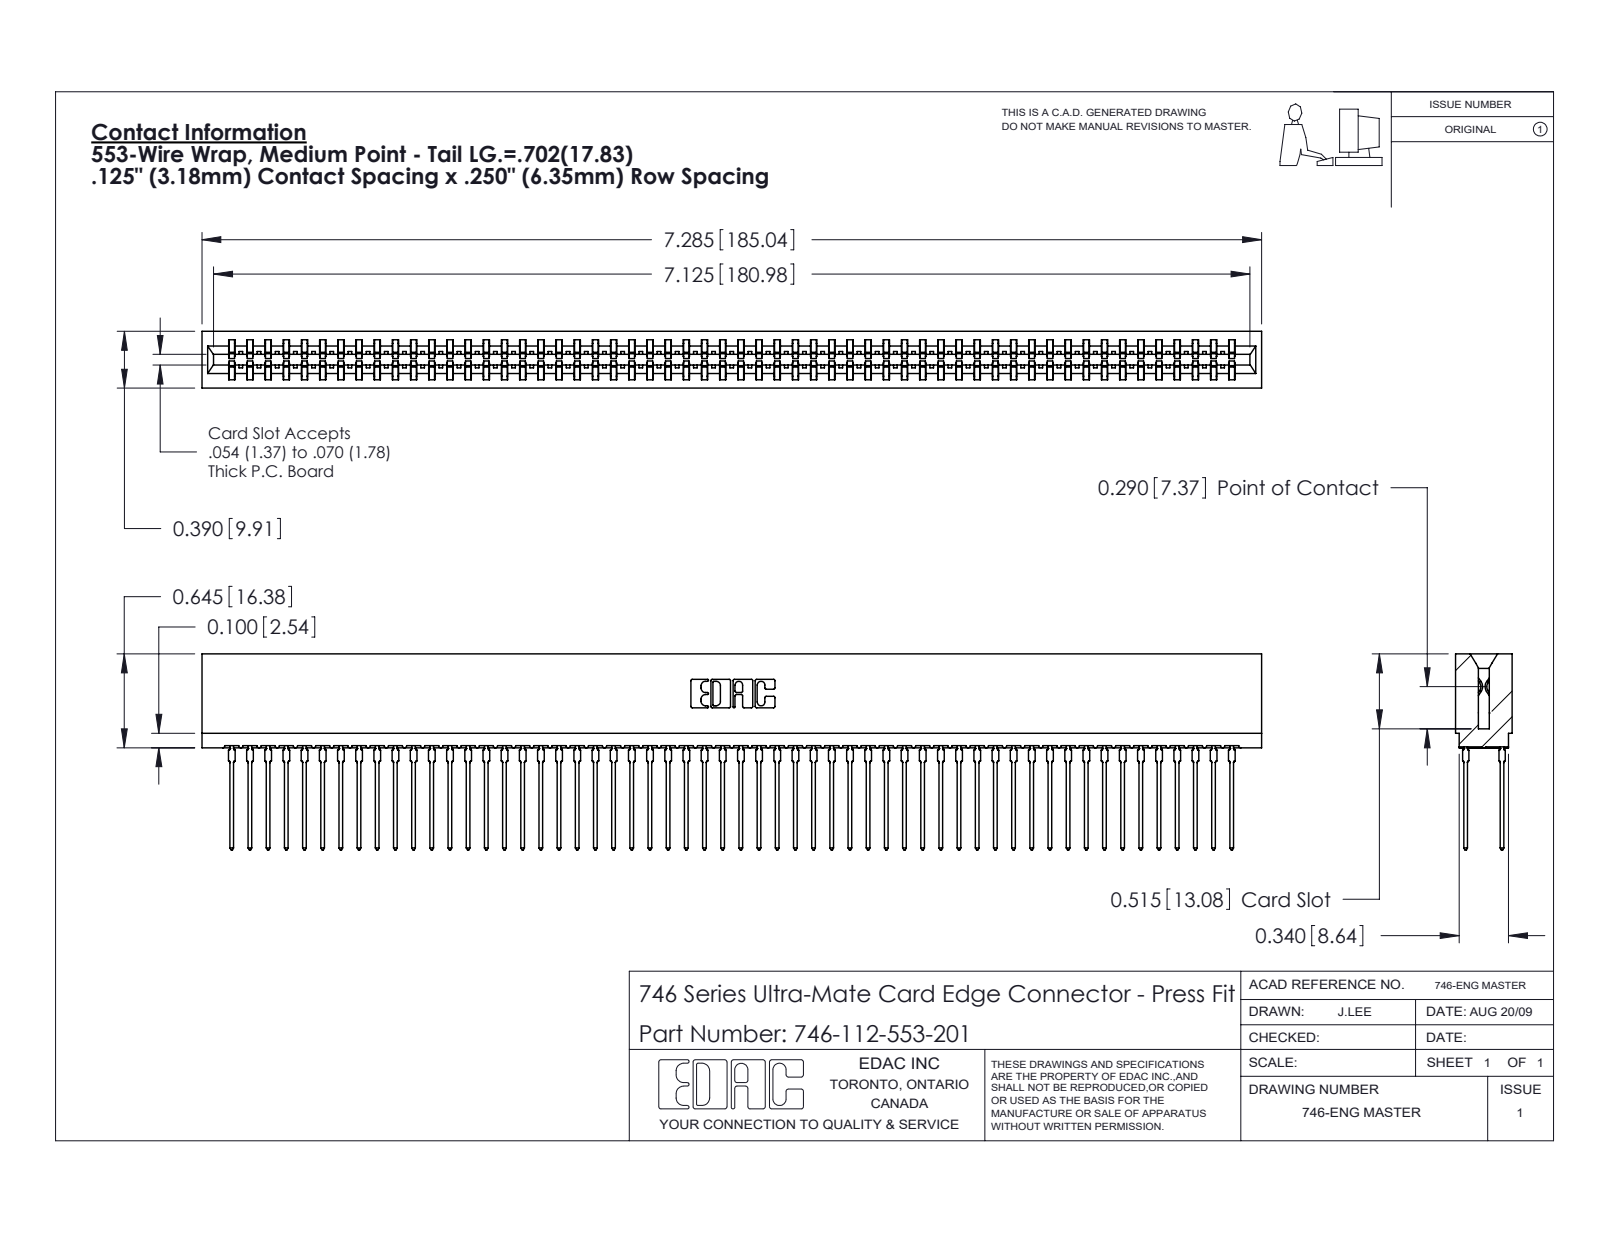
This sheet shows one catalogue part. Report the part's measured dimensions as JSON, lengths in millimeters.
{"part_name": "746-112-553-201; 746-292-001_553; 746 Part_.515 Slot Depth - 01", "step_written_by": "SolidWorks 2020 (CONFIG_CONTROL_DESIGN)", "units": "millimeters", "bodies": {"solids": 113, "faces": 10121, "planar": 5207, "cylindrical": 2002, "other": 2912}, "overall_size": [185, 34.2, 9.9], "volume_mm3": 20240, "surface_area_mm2": 35060, "partial_cylinders_radius": [[0.5, 224], [0.4, 57], [0.3, 22], [0.1, 8], [0.3, 8], [0.2, 6], [0.8, 6], [0.7, 3]], "face_to_face_distances": [1.4, 8.5, 6.4, 0.6, 7.8, 9.9, 2.1, 7, 4.4, 4]}
